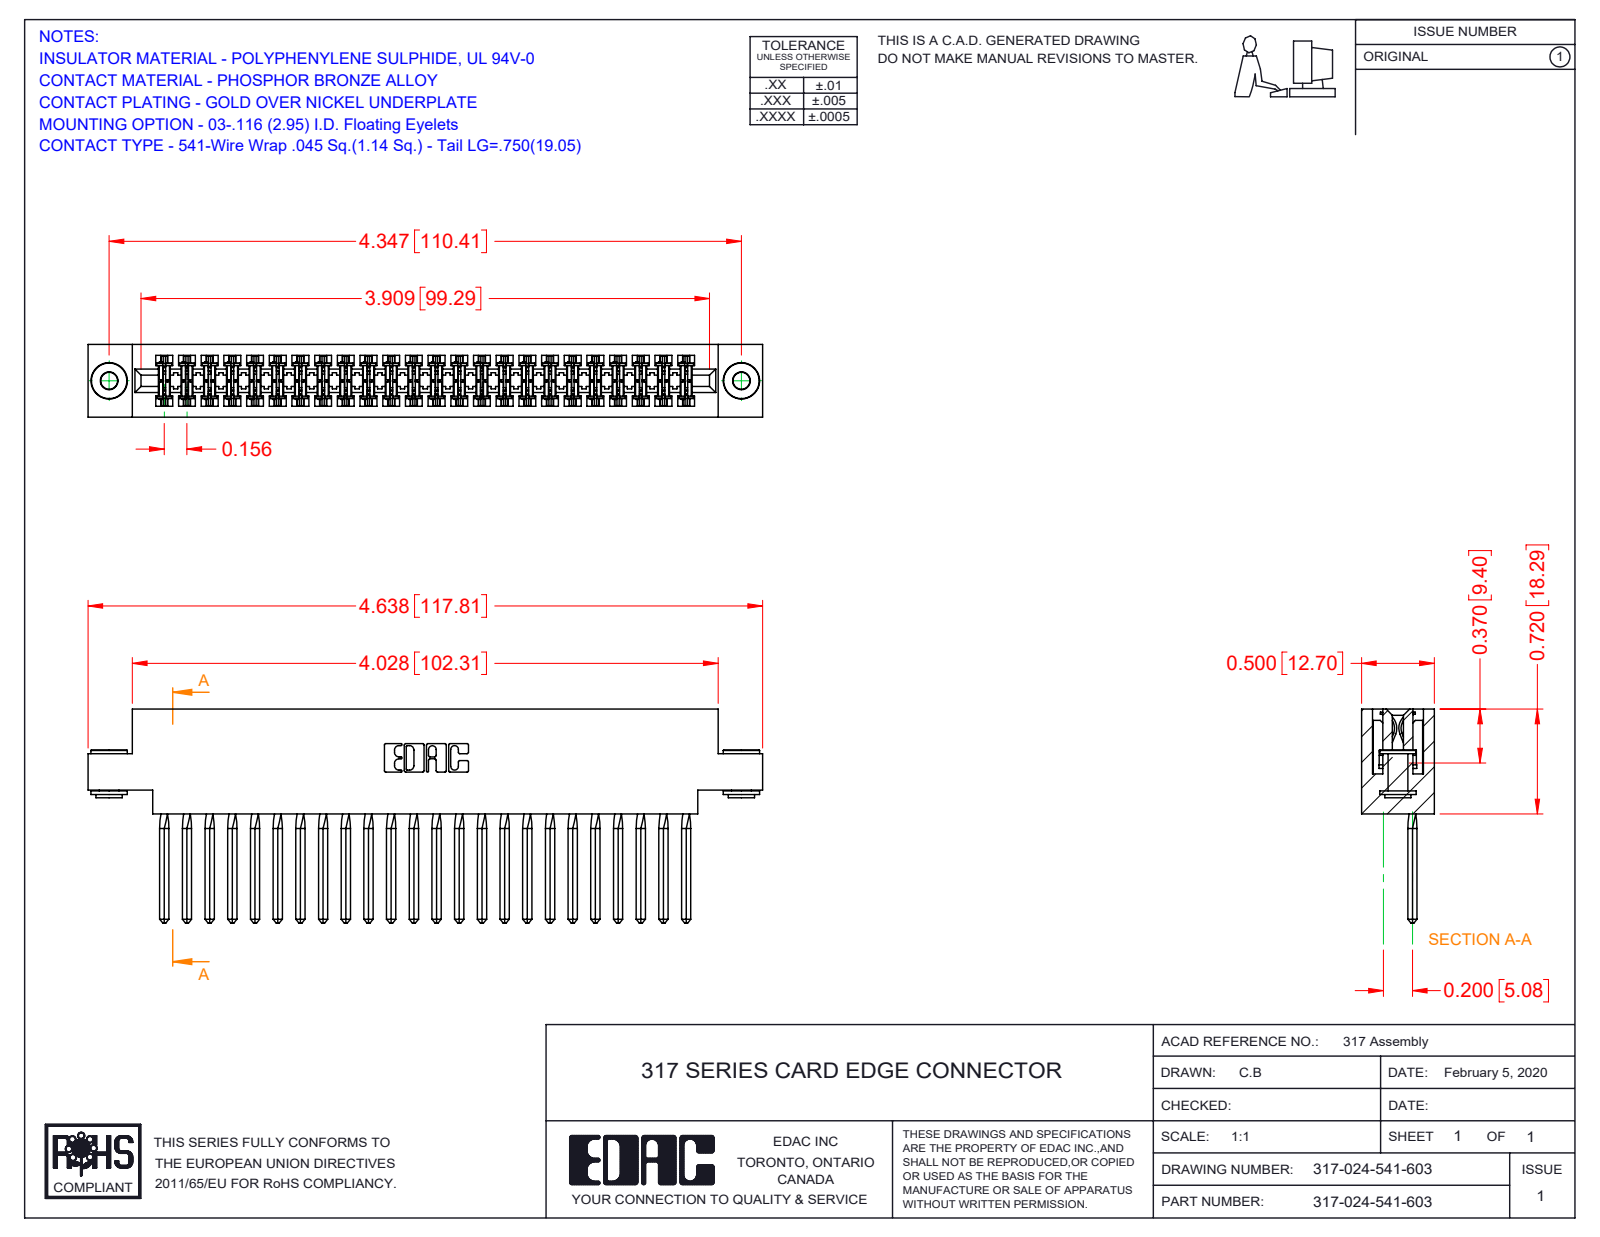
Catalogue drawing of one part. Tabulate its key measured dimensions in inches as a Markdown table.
| quantity | value |
| --- | --- |
| part name | 317-024-541-603; 345-250-002_345-250-002-102; 317-290-002_541; 317 Part_.156 Dia - TH |
| STEP written by | SolidWorks 2016 (CONFIG_CONTROL_DESIGN) |
| units | inches |
| bodies | 27 solids, 3788 faces (3044 planar, 640 cylindrical, 104 other) |
| overall size | 4.638 × 1.47 × 0.5 |
| volume | 1.133 in³ |
| surface area | 40.08 in² |
| round holes (diameter × count) | 0.116 × 2, 0.156 × 2 |
| round bosses / shafts (diameter × count) | 0.25 × 2, 0.18 × 2, 0.136 × 2 |
| partial cylindrical surfaces (radius × count) | 0.015 × 48, 0.01 × 22, 0.007 × 6, 0.031 × 6, 0.026 × 3, 0.095 × 2, 0.1 × 2, 0.11 × 2 |
| main face-to-face distances | 0.5, 0.075, 0.425, 0.11, 0.35, 0.195, 0.772, 0.72, 0.22, 0.211 |
| hole center spacings | 4.347 |
